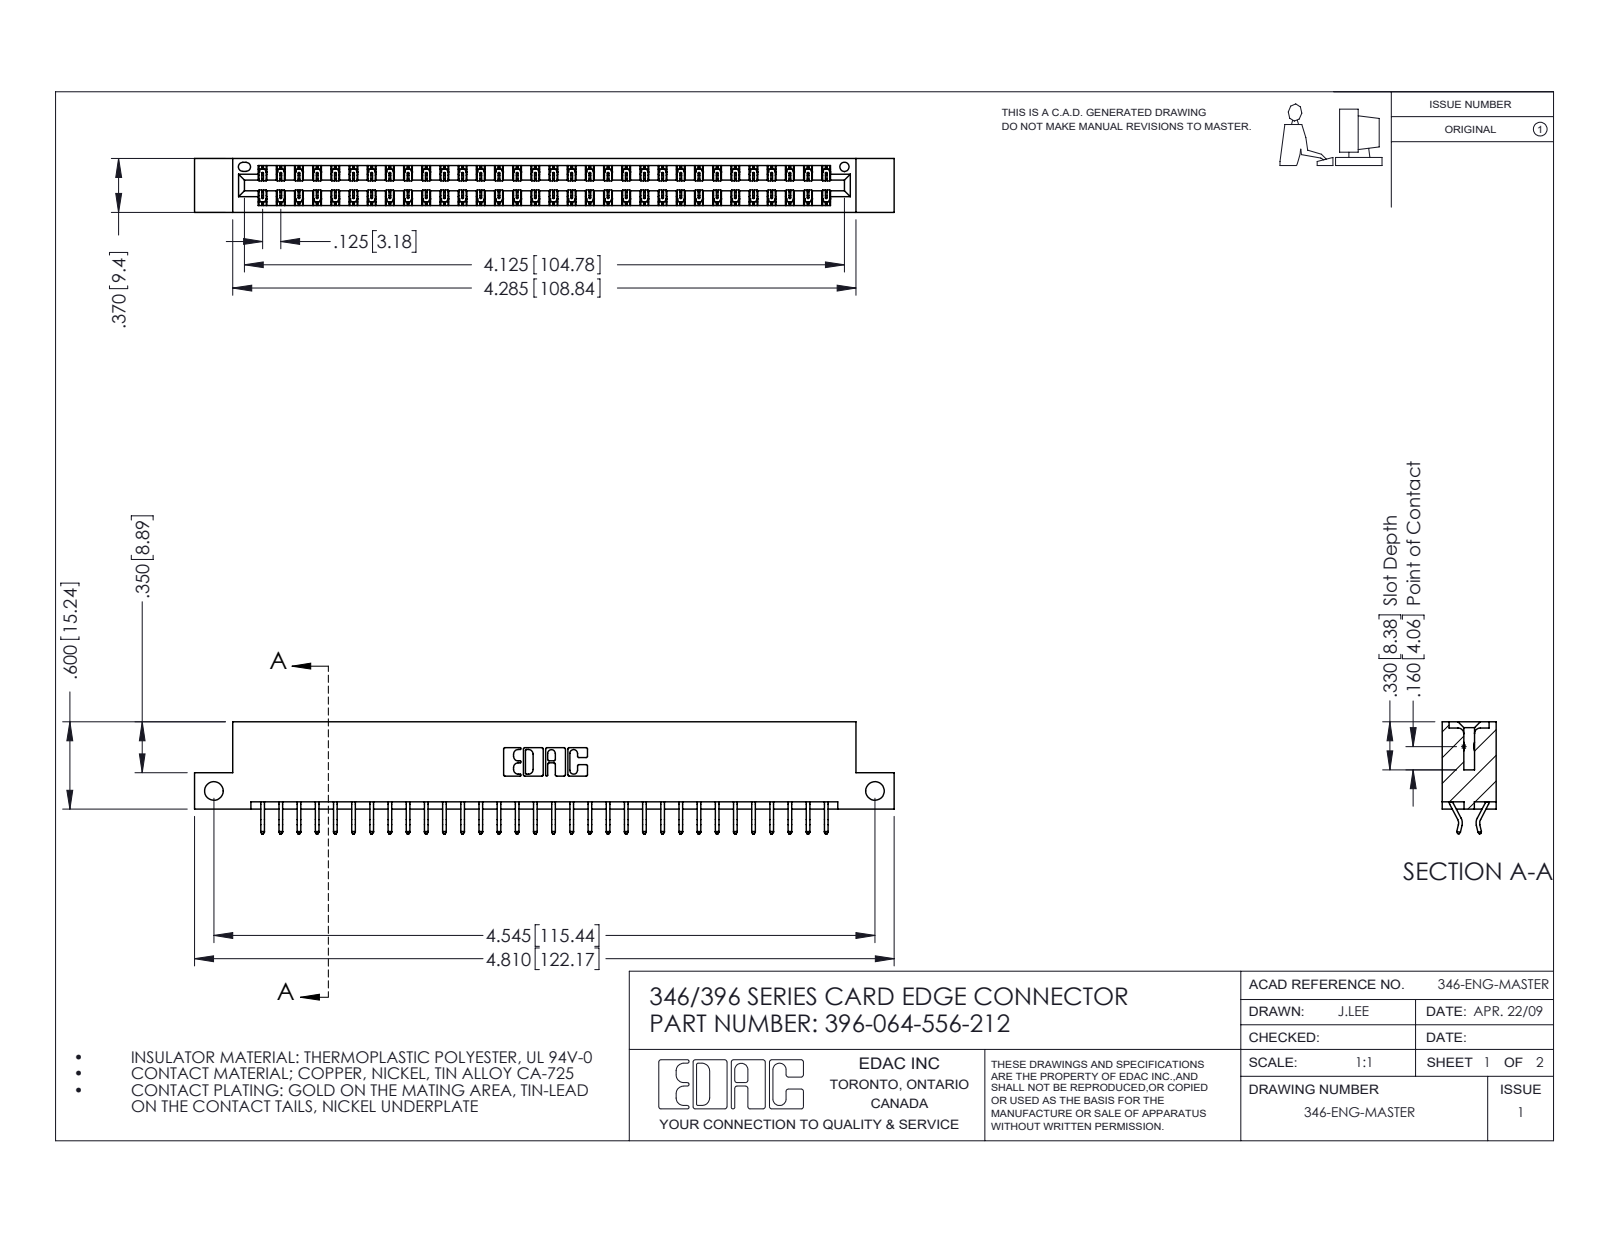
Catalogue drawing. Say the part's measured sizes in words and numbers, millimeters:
The part is named "396-064-556-212; 346 Part_Flush Mounting Lugs - Side Mount; 345-292-001_556 Tail". Its 3-D file was written by "SolidWorks 2016 (CONFIG_CONTROL_DESIGN)". It is 65 solids with 3834 faces: 2572 planar, 1262 cylindrical and 0 other. Overall it measures 122.2 by 19.6 by 9.4 millimeters. Its volume is 11 700 cubic millimeters and its surface area 15 790 square millimeters. Round holes: 2 of diameter 3.3, 1 of diameter 1.6. Partial cylindrical surfaces (rounded edges, fillets, slot ends): 96 of radius 0.2, 22 of radius 0.3, 6 of radius 0.2, 6 of radius 0.8, 3 of radius 0.7, 2 of radius 0.3, 2 of radius 0.4, 2 of radius 0.6. The main face-to-face distances are 1.2, 8.2, 9.4, 6.4, 0.6, 1.8, 7.6, 7, 3.8, 5.6. The hole center spacings are 115.4.
